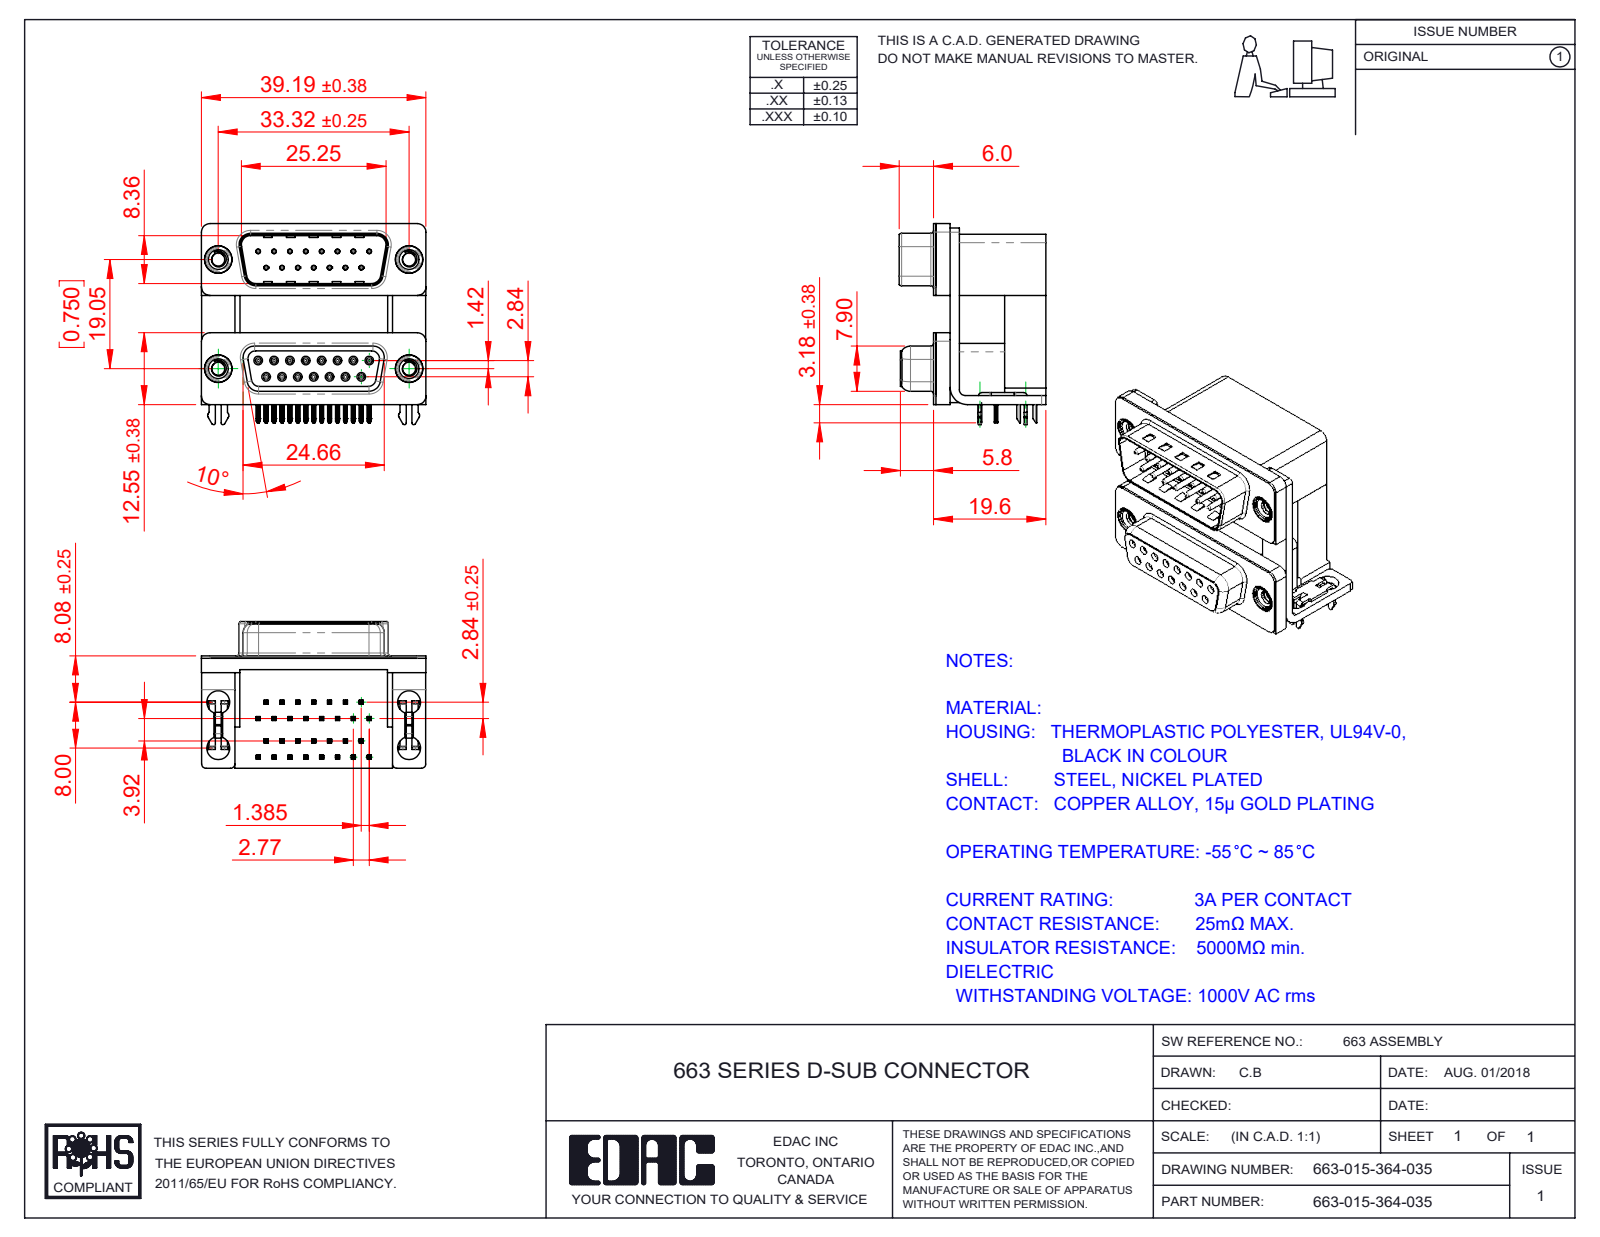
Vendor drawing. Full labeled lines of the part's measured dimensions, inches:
Part name (STEP PRODUCT): 663 Threaded Rivet_4-40; 663 2 Prong Board Lock_3; 663 Contact Top Upper_M; 663 Contact Bottom Upper_M (+8 more)
STEP written by: SolidWorks 2020 (CONFIG_CONTROL_DESIGN)
Units: inches
Bodies: 43 solids, 4064 faces (2117 planar, 1064 cylindrical, 883 other)
Overall size (bounding box): 1.543 × 1.382 × 1.008
Volume: 0.93 in³ · Surface area: 26.34 in²
Round holes (diameter × count): ⌀0.031 ×30, ⌀0.014 ×15, ⌀0.035 ×15, ⌀0.157 ×8, ⌀0.089 ×4, ⌀0.138 ×4, ⌀0.189 ×4, ⌀0.197 ×4
Round bosses / shafts (diameter × count): ⌀0.047 ×15, ⌀0.03 ×15, ⌀0.193 ×4, ⌀0.187 ×4, ⌀0.154 ×4
Partial cylindrical surfaces — rounded edges, fillets, slot ends (radius × count): R0.004 ×122, R0.01 ×70, R0.006 ×60, R0.005 ×30, R0.014 ×30, R0.02 ×16, R0.059 ×16, R0.013 ×15
Main face-to-face distances: 0.016, 0.756, 0.657, 0.098, 0.283, 0.472, 0.374, 0.421, 0.063, 0.114
Hole centre spacings: 0.124, 0.758, 0.109, 0.781, 0.218, 0.327, 0.75, 0.818
